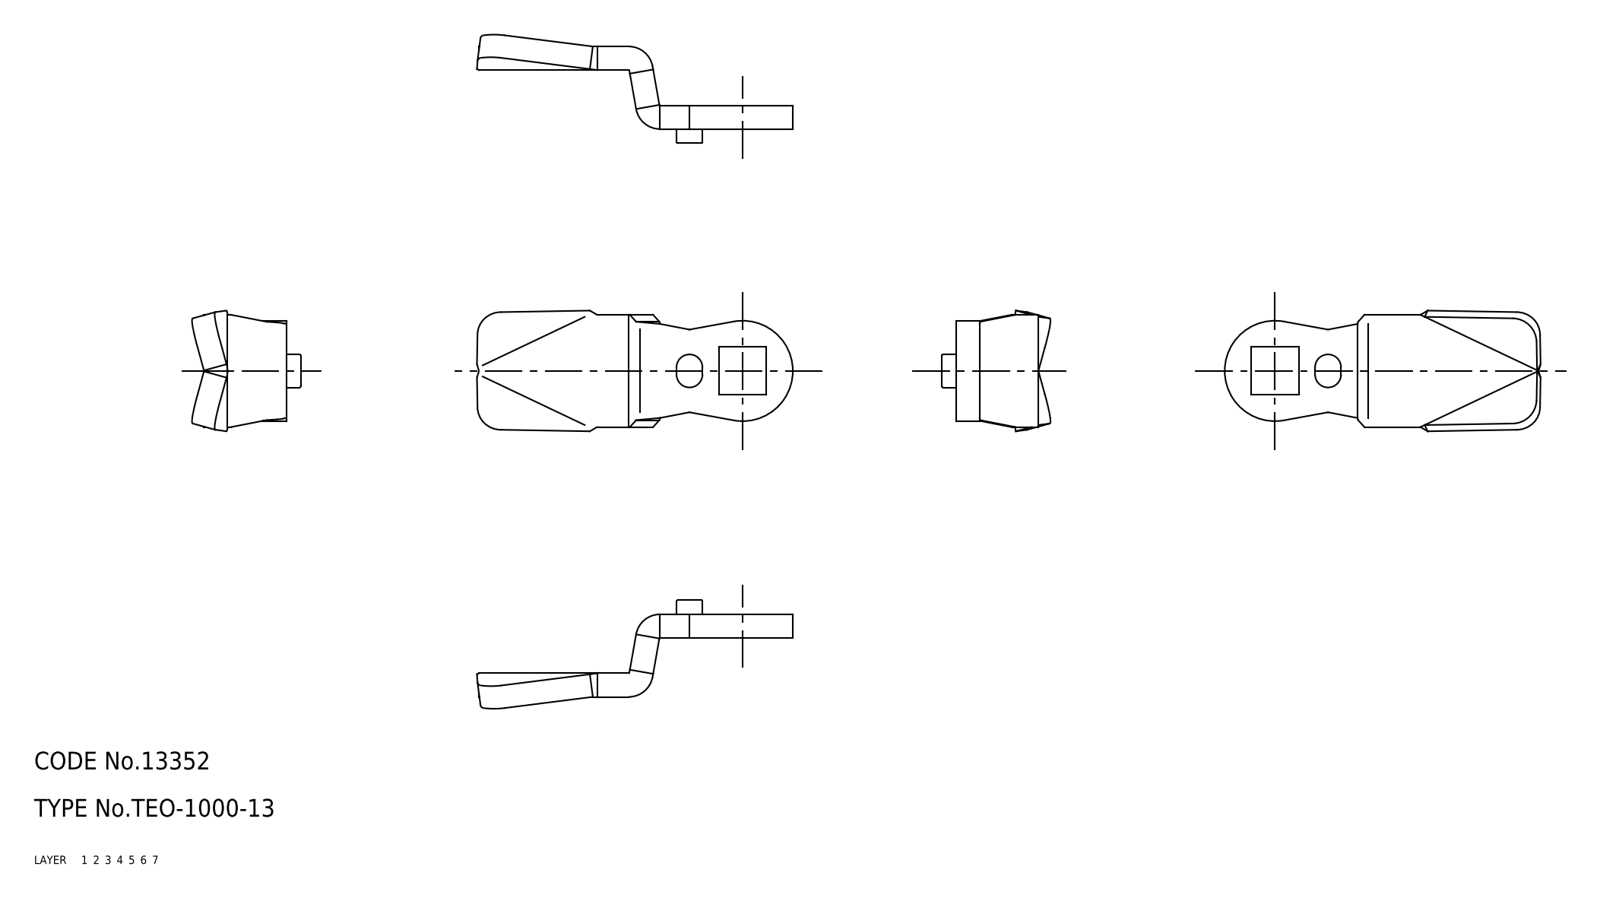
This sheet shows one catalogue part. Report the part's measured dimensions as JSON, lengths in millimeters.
{"part_name": "cam", "step_written_by": "CADfix (AUTOMOTIVE_DESIGN)", "units": "millimeters", "bodies": {"solids": 1, "faces": 55, "planar": 0, "cylindrical": 0, "other": 55}, "overall_size": [53.96, 20.94, 19.86], "volume_mm3": 3991, "surface_area_mm2": 2817}
